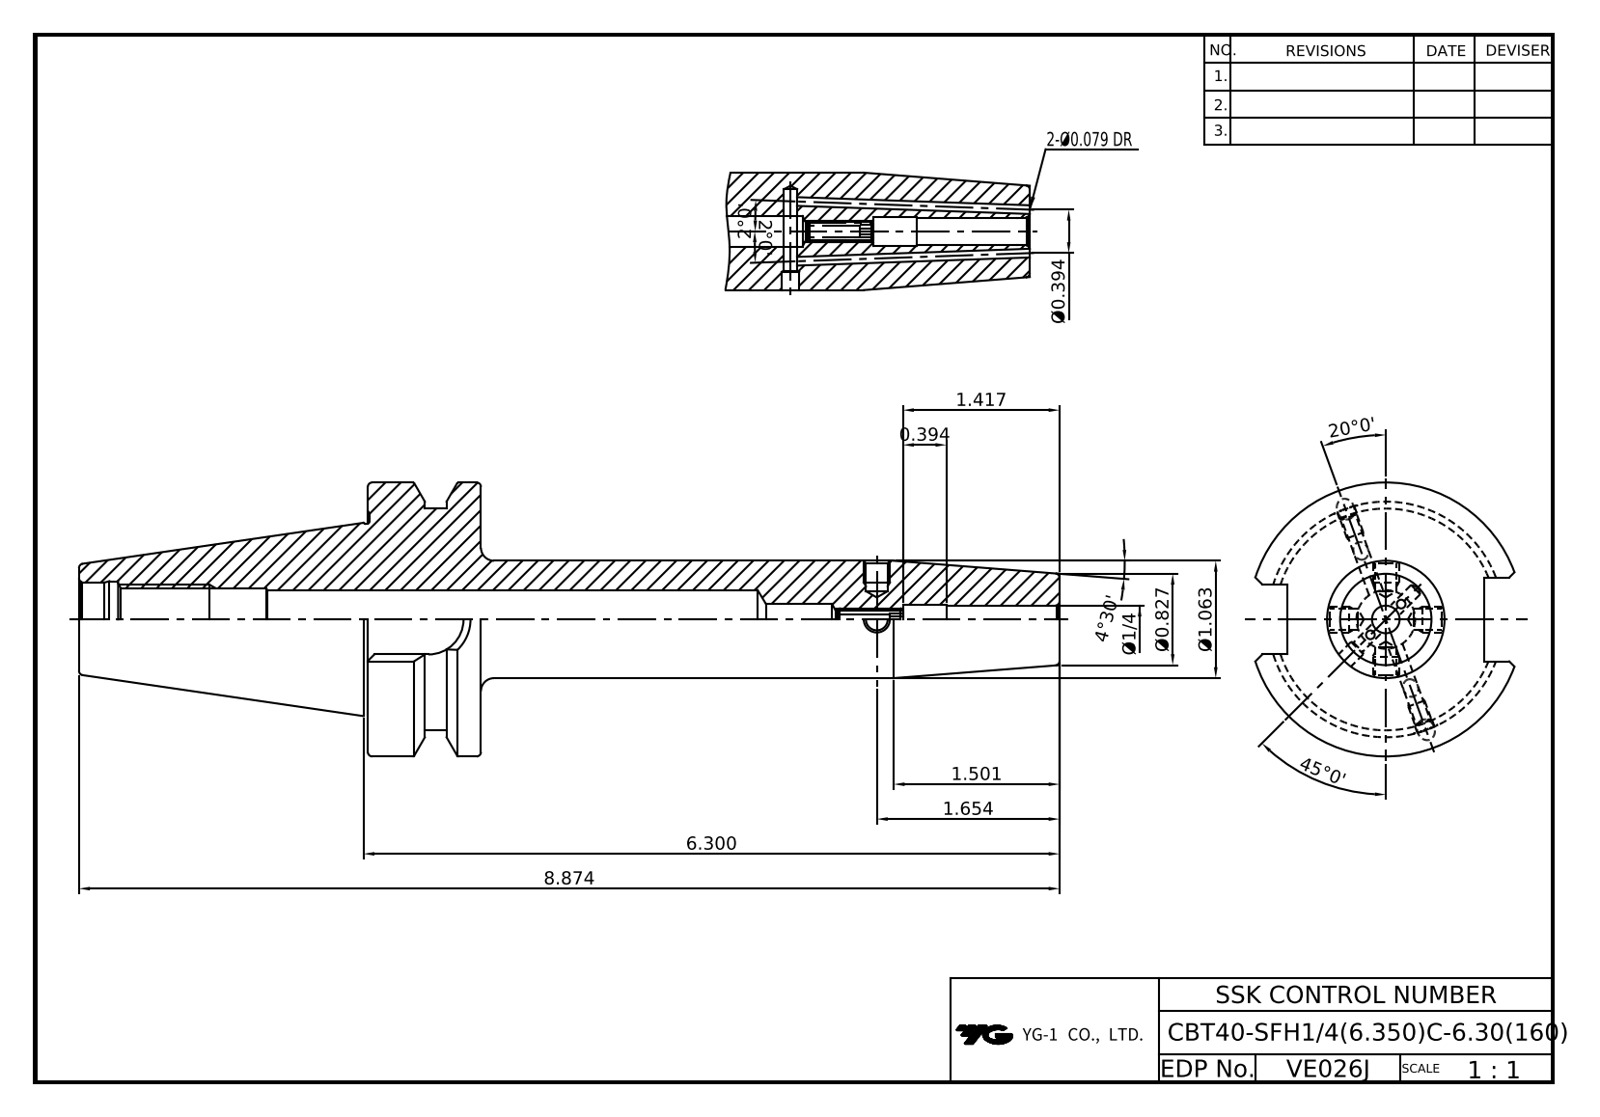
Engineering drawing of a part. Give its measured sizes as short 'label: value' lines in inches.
name: CBT40-SFH6_35C-160
written by: CREO PARAMETRIC BY PTC INC, 2018500 (CONFIG_CONTROL_DESIGN)
unit: in
bodies: 1 solid, 96 faces (22 planar, 30 cylindrical, 44 other)
size: 8.874 × 2.48 × 2.48
volume: 10.96 in³; area: 59.78 in²
holes: 1× ⌀0.197, 1× ⌀0.25, 1× ⌀0.266, 1× ⌀0.276, 1× ⌀0.531, 1× ⌀0.551, 1× ⌀0.63, 1× ⌀0.669, 1× ⌀0.693
bosses: 1× ⌀2.48, 1× ⌀2.008, 1× ⌀1.732, 1× ⌀1.063
rounds: 1× R0.317
face distances: 0.984, 1.78, 6.22, 5.236, 0.673, 0.311, 5.547, 0.476, 0.197, 0.508
